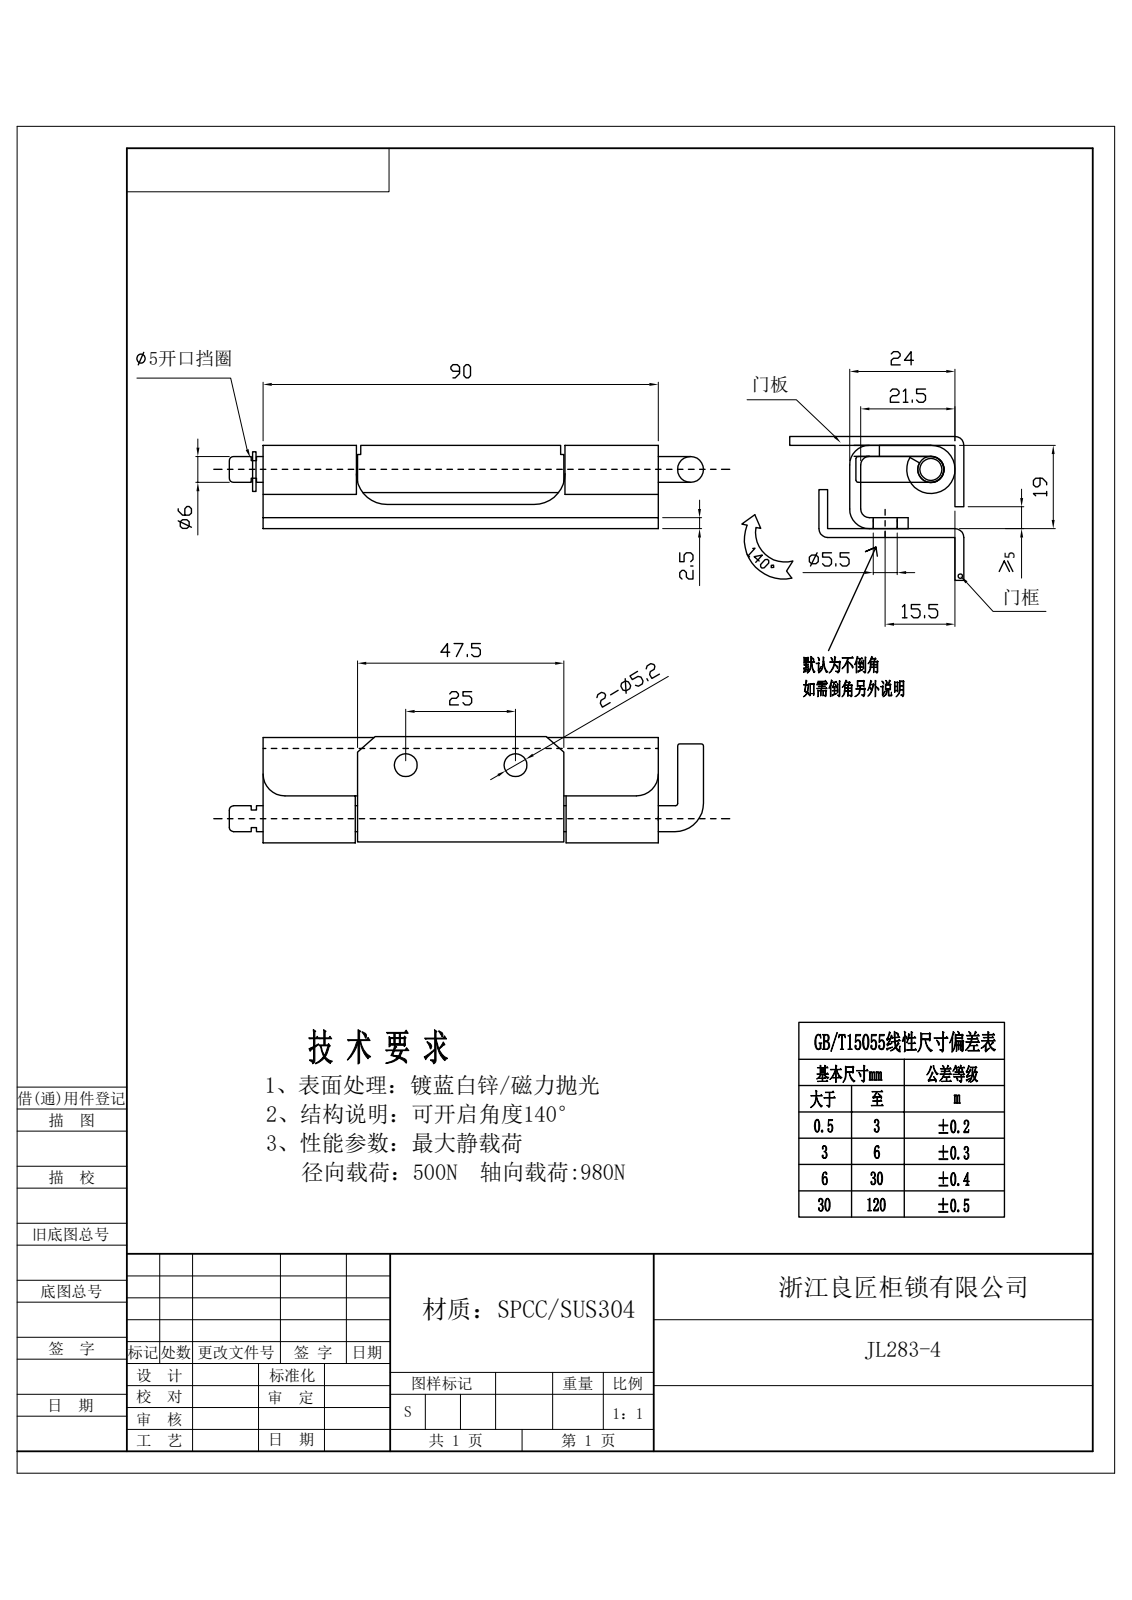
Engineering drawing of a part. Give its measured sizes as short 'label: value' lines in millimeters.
written by: Rhino 8.5 (CONFIG_CONTROL_DESIGN)
unit: mm
bodies: 3 solids, 66 faces (30 planar, 32 cylindrical, 4 other)
size: 108 × 24 × 22.05
volume: 16 416 mm³; area: 14 407 mm²
holes: 2× ⌀5.2, 1× ⌀6
bosses: 2× ⌀5.9, 1× ⌀11, 1× ⌀4
rounds: 2× R2, 2× R4.5, 2× R5, 2× R7
face distances: 2.5, 16.5, 19, 14, 21.25, 68.75, 13.3, 10.8, 21.5, 68.5
hole spacings: 25
